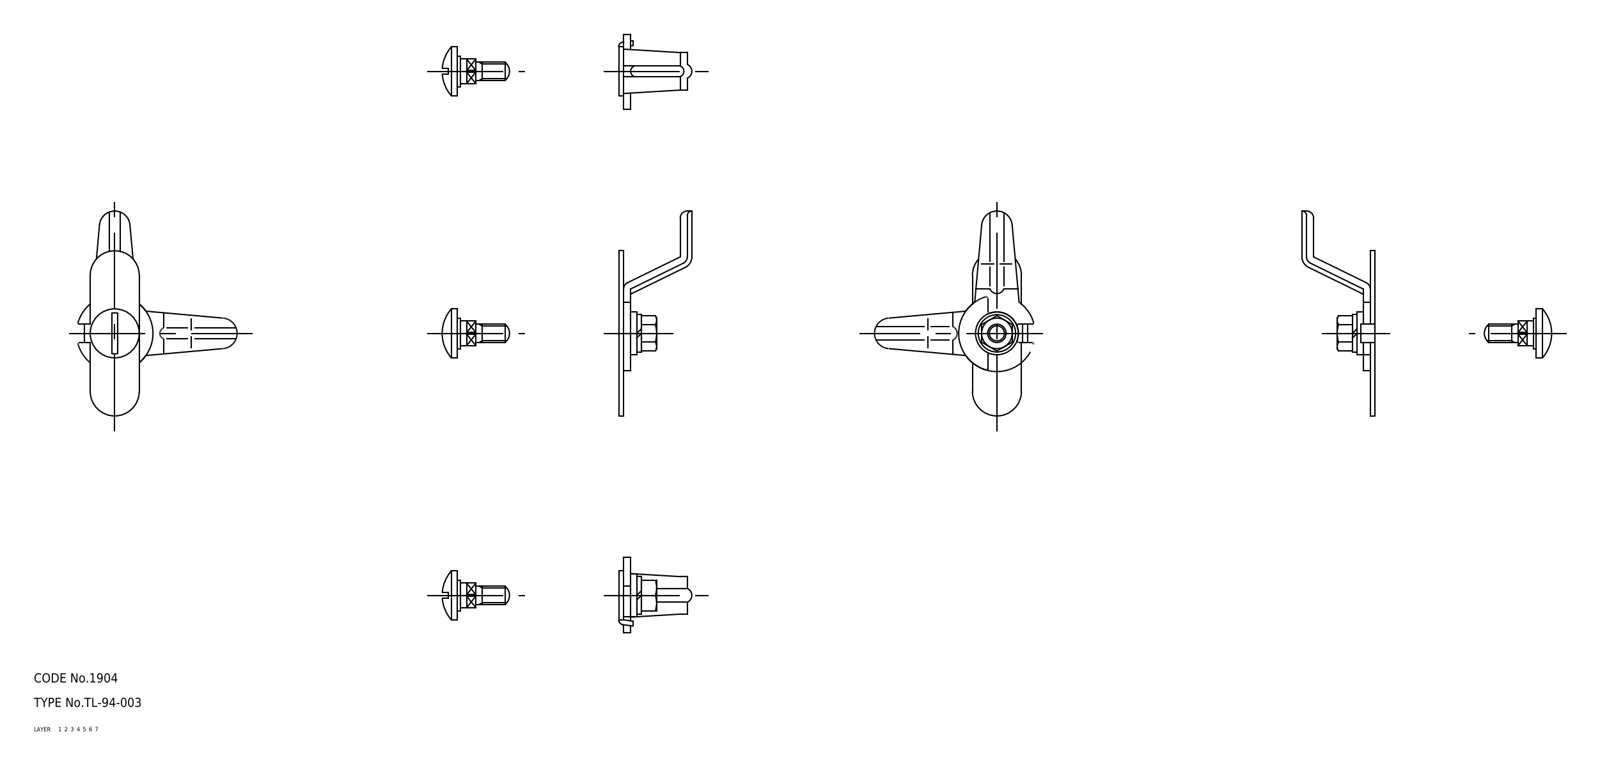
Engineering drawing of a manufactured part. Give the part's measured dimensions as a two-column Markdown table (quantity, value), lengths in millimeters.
| quantity | value |
| --- | --- |
| part name | washer; nut; knob; cam (+2 more) |
| STEP written by | CADfix (AUTOMOTIVE_DESIGN) |
| units | millimeters |
| bodies | 5 solids, 116 faces (0 planar, 0 cylindrical, 116 other) |
| overall size | 67 × 30.97 × 24.48 |
| volume | 5 043 mm³ |
| surface area | 5 762 mm² |
